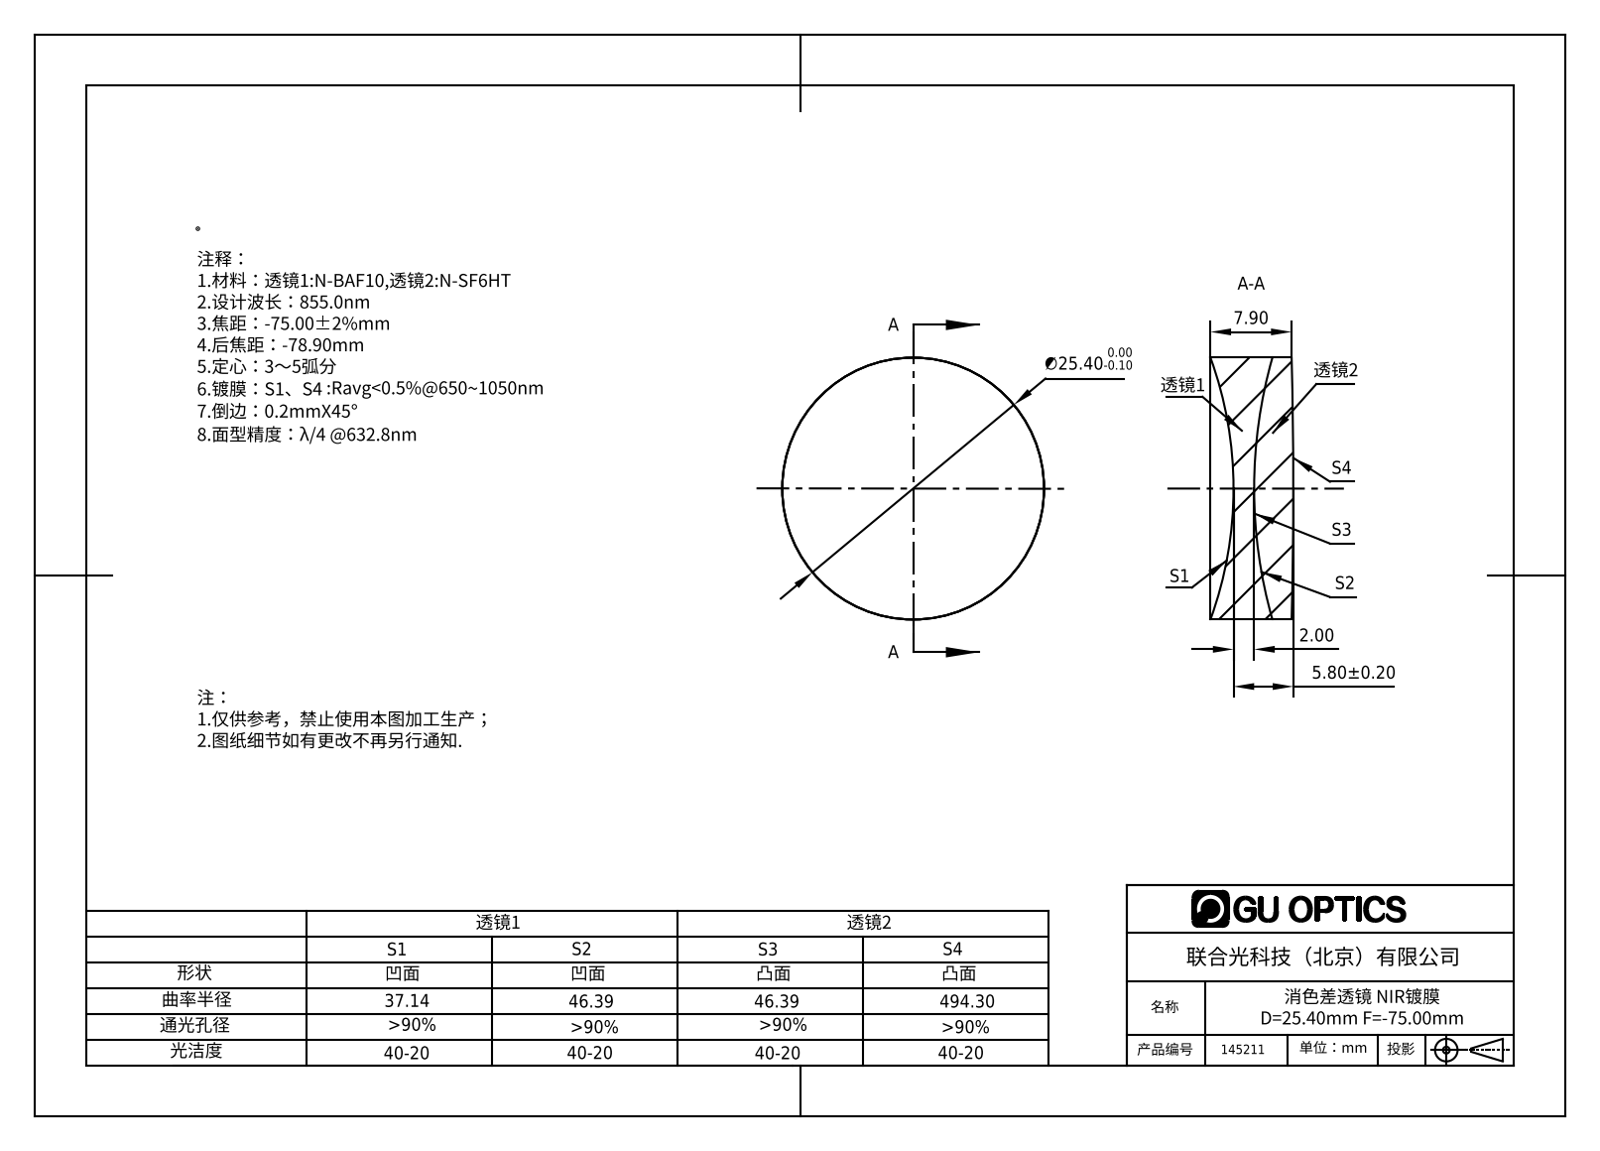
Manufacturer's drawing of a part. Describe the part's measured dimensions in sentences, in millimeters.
The part is named "145211". Its 3-D file was written by "SolidWorks 2016 (AUTOMOTIVE_DESIGN)". It is 2 solids with 12 faces: 0 planar, 4 cylindrical and 8 other. Overall it measures 25.4 by 25.4 by 8.04 millimeters. Its volume is 3 459 cubic millimeters and its surface area 2 691 square millimeters. Round bosses or shafts: 1 of diameter 25.4.
